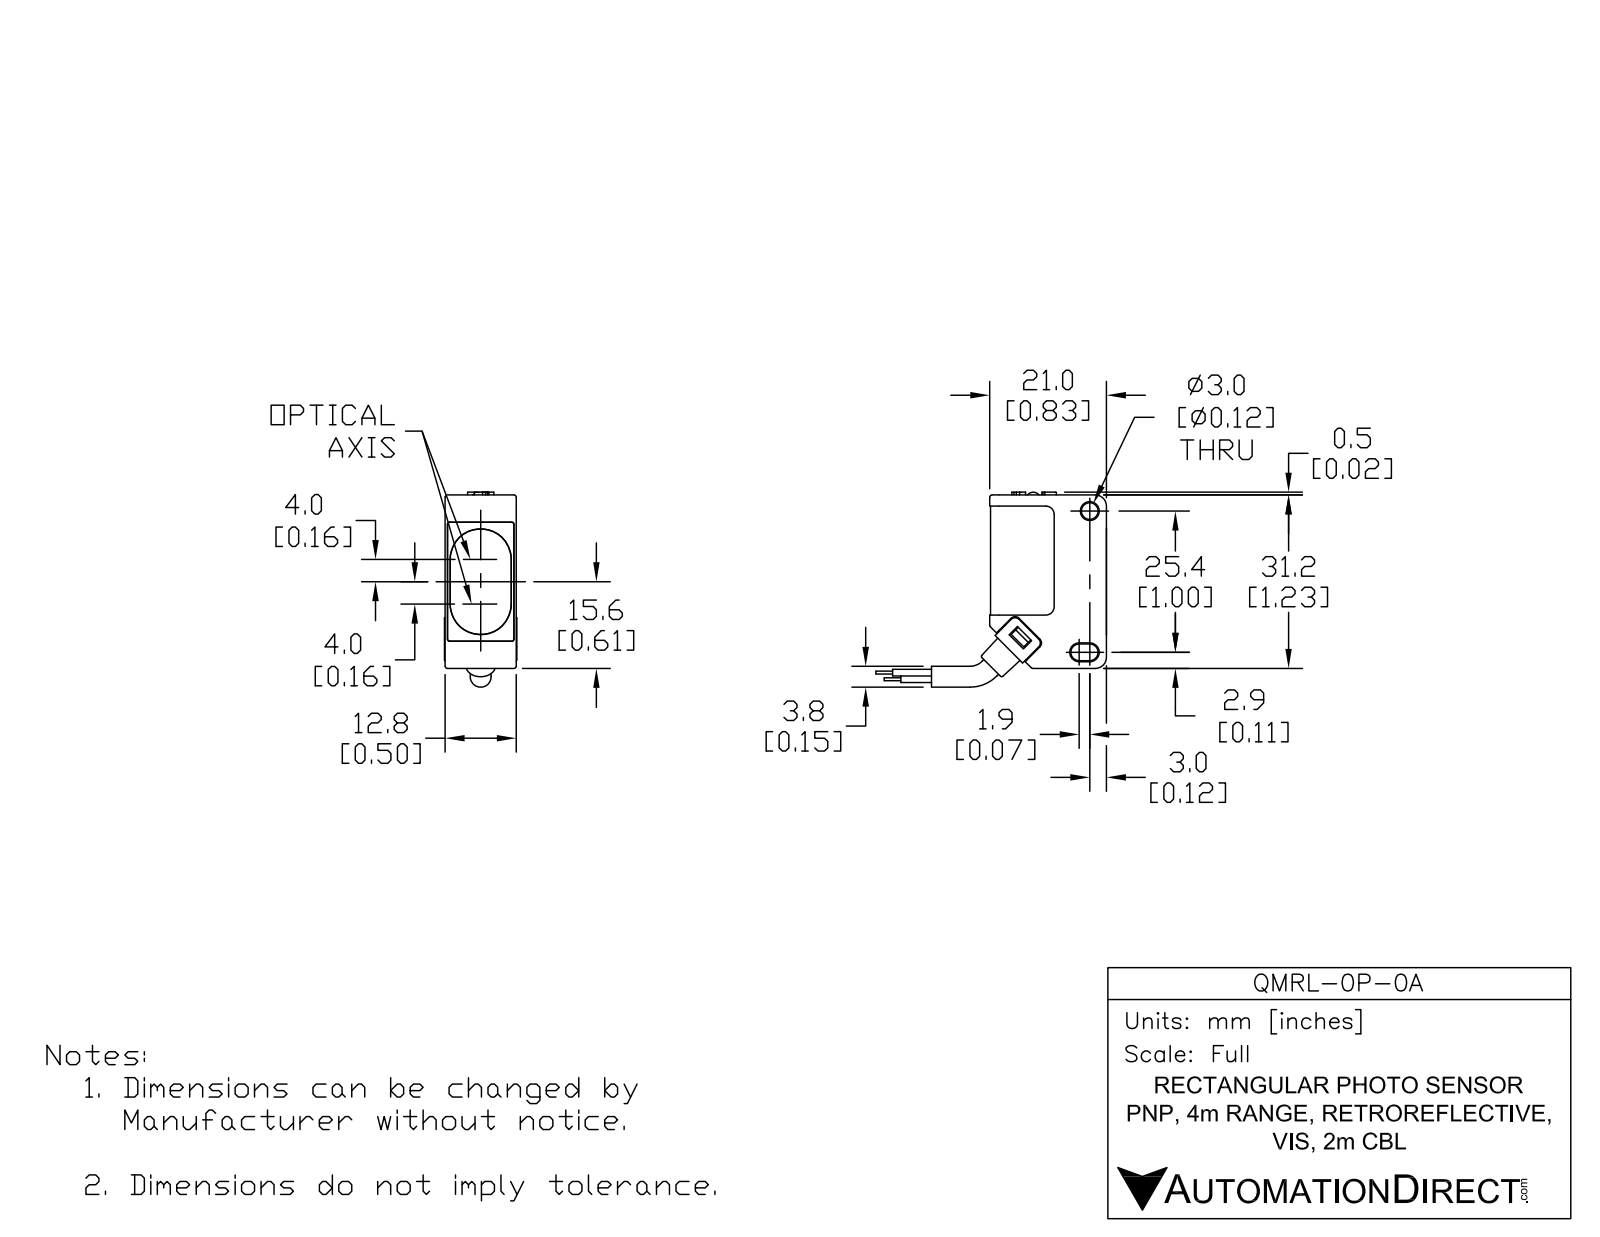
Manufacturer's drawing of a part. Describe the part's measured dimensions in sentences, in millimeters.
The part is named "QMRL-0P-0A". Its 3-D file was written by "SolidWorks 2017 (AUTOMOTIVE_DESIGN)". It is 9 solids with 258 faces: 134 planar, 100 cylindrical and 24 other. Overall it measures 81.1 by 26.2 by 13 millimeters. Its volume is 7 700 cubic millimeters and its surface area 5 403 square millimeters. Round holes: 3 of diameter 3, 1 of diameter 3.8, 1 of diameter 5.7, 1 of diameter 7.2. Round bosses or shafts: 2 of diameter 3.5. Partial cylindrical surfaces (rounded edges, fillets, slot ends): 13 of radius 0.4, 10 of radius 0.5, 8 of radius 1, 6 of radius 1.5, 4 of radius 0.6, 2 of radius 0.2, 2 of radius 0.9, 2 of radius 1.1. The main face-to-face distances are 0.5, 12.6, 1.5, 0.4, 12.8, 3.5, 12.4, 2, 12.2, 12.5. The hole center spacings are 5.2.
